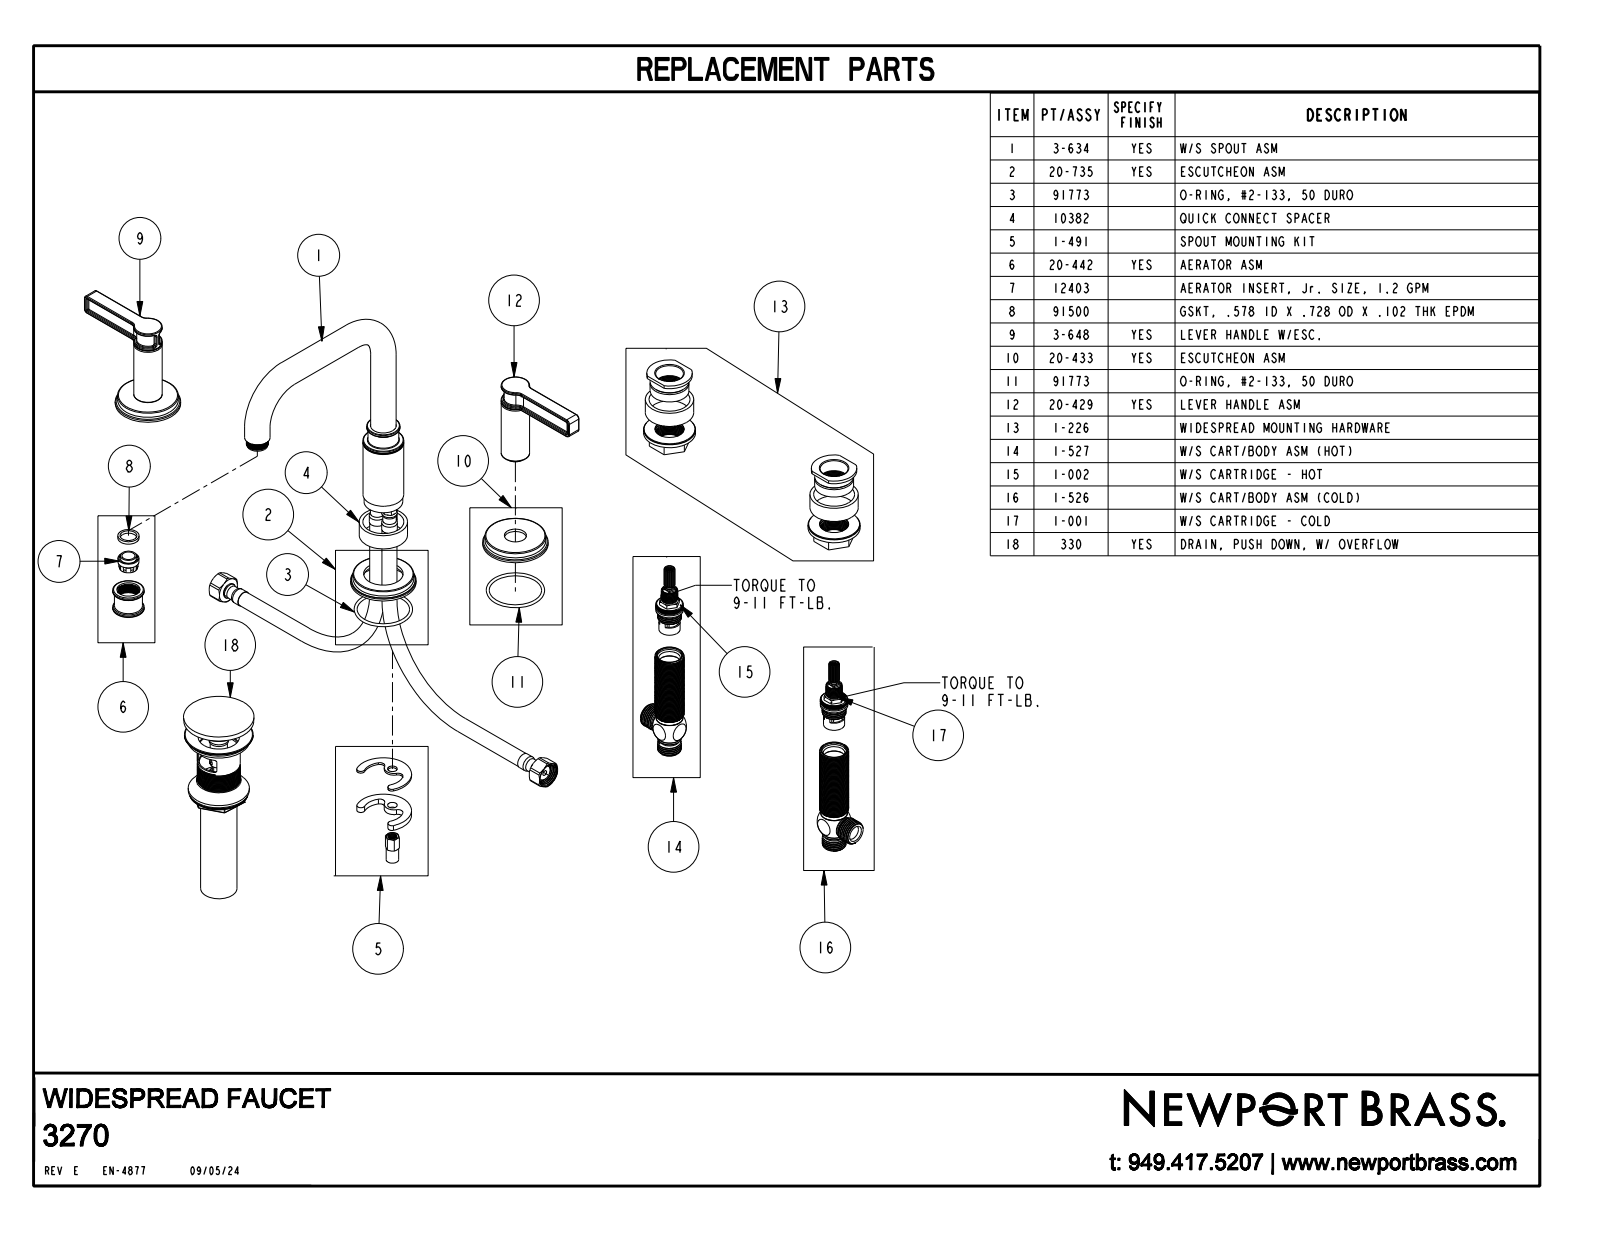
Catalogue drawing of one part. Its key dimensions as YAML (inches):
part_name: "3270"
step_written_by: "CREO PARAMETRIC BY PTC INC, 2018400 (CONFIG_CONTROL_DESIGN)"
units: inches
bodies: {solids: 3, faces: 317, planar: 45, cylindrical: 126, other: 146}
overall_size: [13.7, 8.197, 7.79]
volume: 20.54
surface_area: 110.2
round_bosses_or_shafts:
  - {diameter: 2.25, count: 3}
  - {diameter: 2.09, count: 3}
  - {diameter: 0.875, count: 3}
  - {diameter: 0.975, count: 2}
  - {diameter: 0.85, count: 2}
  - {diameter: 0.506, count: 2}
  - {diameter: 1.4, count: 1}
  - {diameter: 1.14, count: 1}
partial_cylinders:
  - {radius: 0.025, count: 32}
  - {radius: 0.03, count: 4}
  - {radius: 0.1, count: 4}
  - {radius: 0.13, count: 4}
  - {radius: 0.25, count: 4}
  - {radius: 0.35, count: 4}
  - {radius: 0.387, count: 2}
face_to_face_distances: [0.35, 3.251, 2.901, 2.551, 2.201, 0.7, 0.1, 0.3, 0.6, 0.5]
